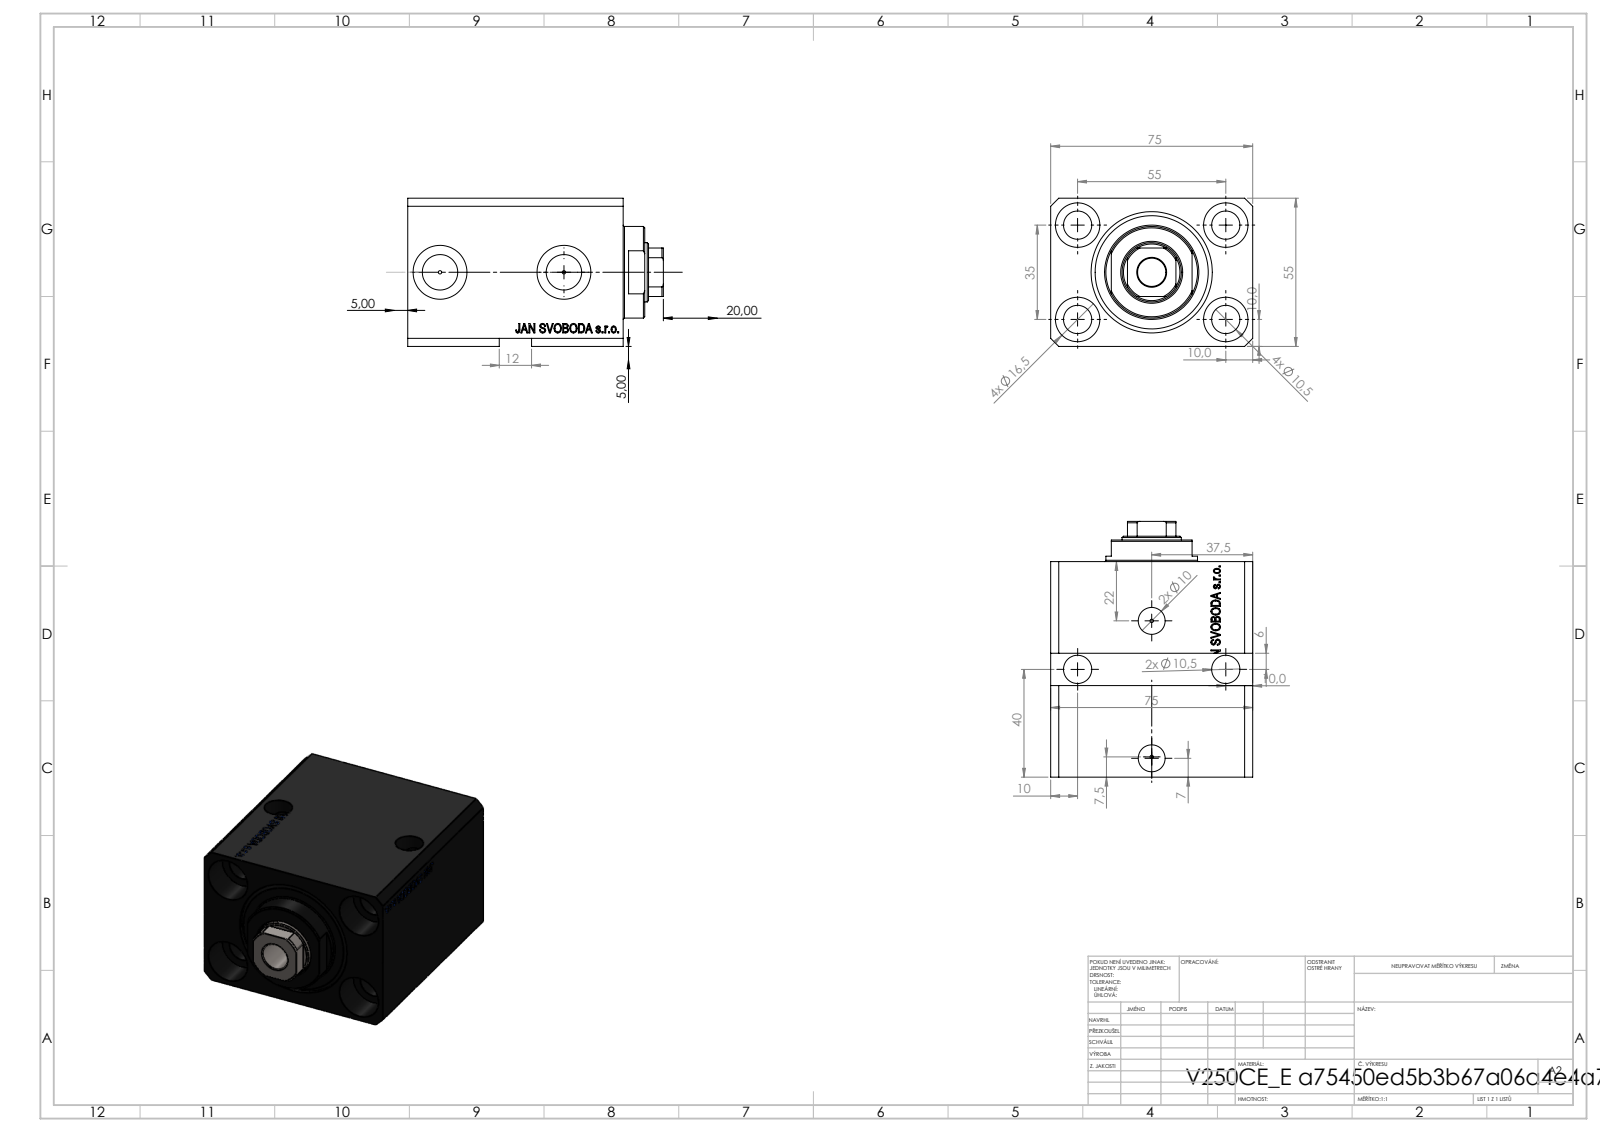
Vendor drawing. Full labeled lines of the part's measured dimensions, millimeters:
Part name (STEP PRODUCT): V250CE_C_VCP; V250CE_E_Body; V250CE_VC_E
STEP written by: SolidWorks 2019 (CONFIG_CONTROL_DESIGN)
Units: millimetres
Bodies: 3 solids, 894 faces (438 planar, 84 cylindrical, 372 other)
Overall size (bounding box): 95 × 75 × 55
Volume: 275 455 mm³ · Surface area: 67 234 mm²
Round holes (diameter × count): ⌀10.5 ×7, ⌀1.25 ×4, ⌀16.5 ×4, ⌀10 ×2, ⌀13.16 ×2, ⌀20 ×2, ⌀22 ×1, ⌀32 ×1, ⌀45 ×1
Round bosses / shafts (diameter × count): ⌀34 ×1
Partial cylindrical surfaces — rounded edges, fillets, slot ends (radius × count): R10.5 ×1
Main face-to-face distances: 55, 75, 15, 80, 65, 9.9, 55.1, 70.1, 11, 69
Hole centre spacings: 32.6, 55, 32.87, 35, 42.55, 42.96, 65.19, 0.53
